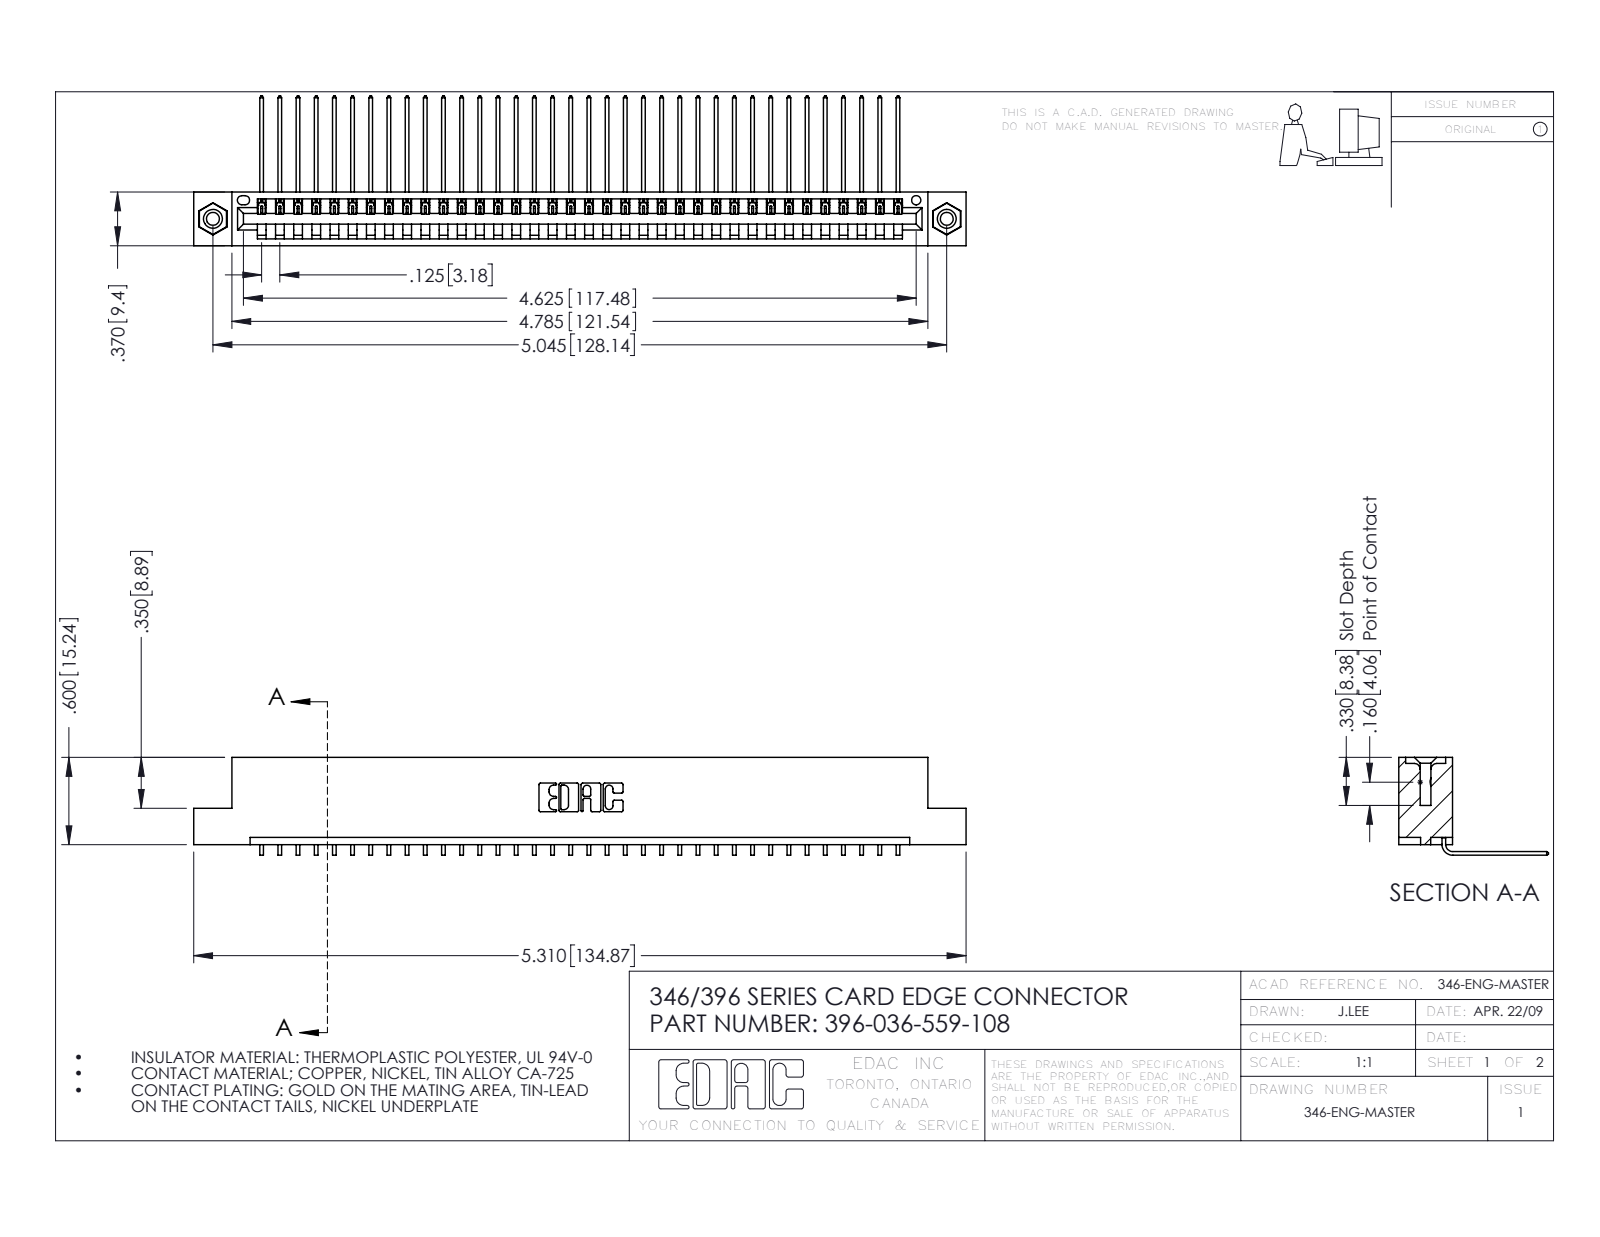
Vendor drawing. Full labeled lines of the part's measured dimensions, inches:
Part name (STEP PRODUCT): 346 Part_Flush Mounting Lugs - 0.156 Dia-TI; 396-036-559-108; 345-250-001_345-250-003-102; 345-292-001_558 559 Tail - 1
STEP written by: SolidWorks 2016 (CONFIG_CONTROL_DESIGN)
Units: inches
Bodies: 39 solids, 2342 faces (1620 planar, 706 cylindrical, 16 other)
Overall size (bounding box): 5.31 × 1.03 × 0.673
Volume: 0.792 in³ · Surface area: 26.19 in²
Round holes (diameter × count): ⌀0.089 ×2, ⌀0.125 ×2, ⌀0.156 ×2, ⌀0.064 ×1
Round bosses / shafts (diameter × count): ⌀0.155 ×2
Partial cylindrical surfaces — rounded edges, fillets, slot ends (radius × count): R0.006 ×72, R0.01 ×22, R0.007 ×6, R0.031 ×6, R0.026 ×3, R0.031 ×2, R0.04 ×2, R0.014 ×1
Main face-to-face distances: 0.048, 0.322, 0.37, 0.25, 0.025, 0.072, 0.298, 0.148, 0.222, 0.1
Hole centre spacings: 0.246, 4.836, 5.045
